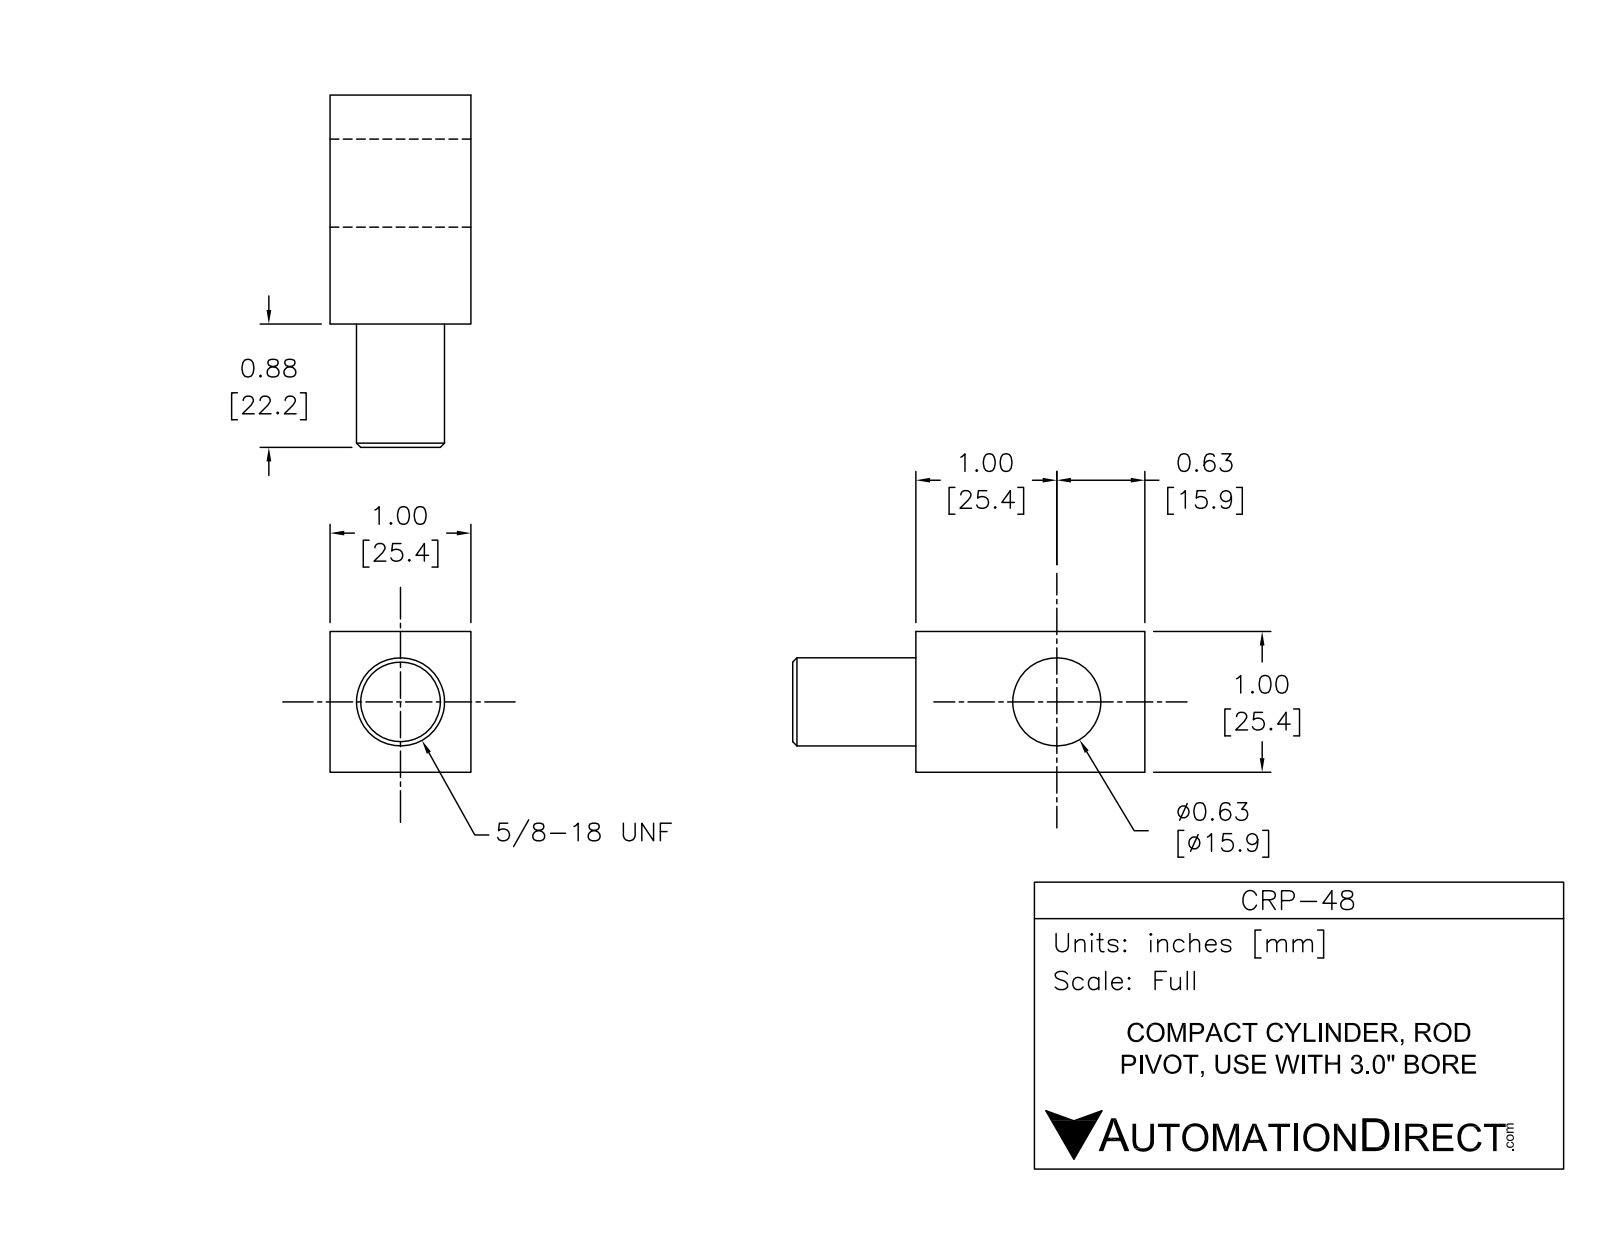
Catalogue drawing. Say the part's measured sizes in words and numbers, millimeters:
The part is named "CRP-48". Its 3-D file was written by "SolidWorks 2014 (AUTOMOTIVE_DESIGN)". It is 1 solid with 13 faces: 7 planar, 4 cylindrical and 2 other. Overall it measures 63.8 by 25.4 by 25.4 millimeters. Its volume is 23 840 cubic millimeters and its surface area 7 516 square millimeters. Round holes: 1 of diameter 19.1. Round bosses or shafts: 1 of diameter 15.9. The main face-to-face distances are 25.4, 41.4, 22.4, 63.8.
